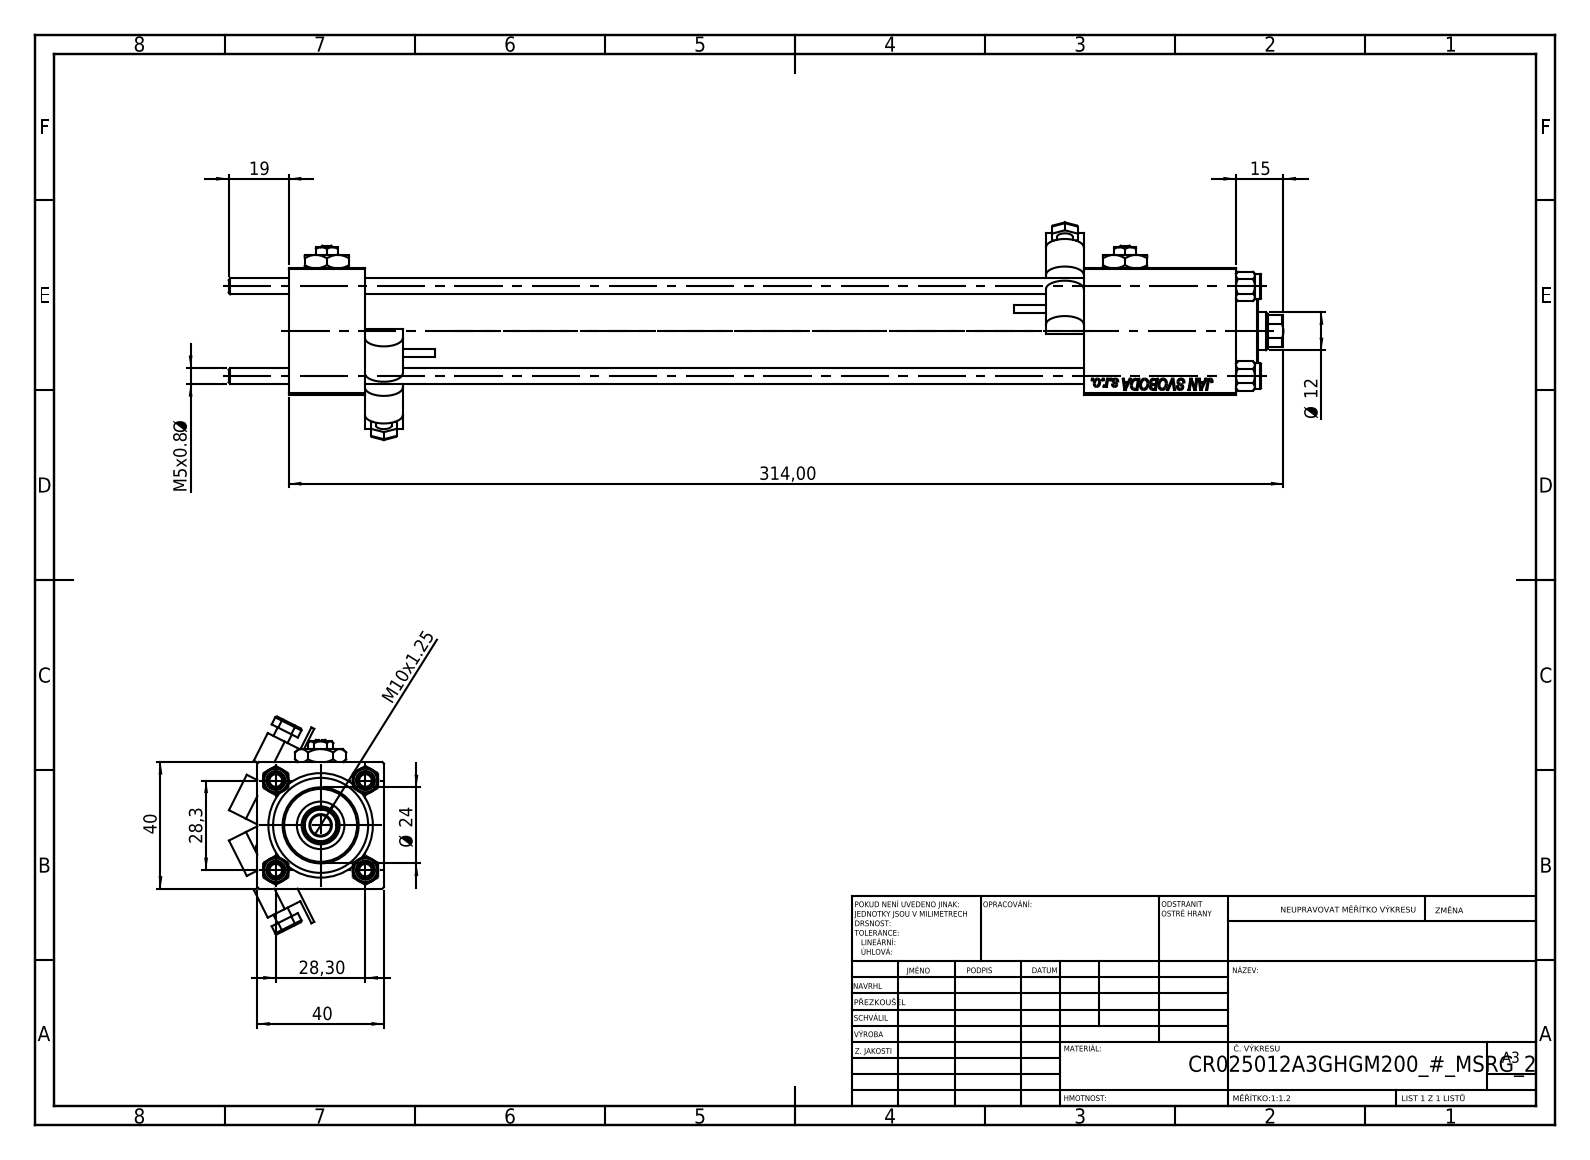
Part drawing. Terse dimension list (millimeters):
name: V215_VC_A; MSRF_MSRG1; Zatka_pro_OIL_PORT; CR025_012_A_0_G_A_G_M_020_+#_##_TYCINKA (+3 more)
written by: SolidWorks 2019 (CONFIG_CONTROL_DESIGN)
unit: mm
bodies: 15 solids, 1296 faces (600 planar, 118 cylindrical, 578 other)
size: 333 × 68.71 × 48.93
volume: 232 318 mm³; area: 114 553 mm²
holes: 4× ⌀5, 3× ⌀20, 2× ⌀7, 2× ⌀13.16, 1× ⌀6.5, 1× ⌀12, 1× ⌀15, 1× ⌀25, 1× ⌀30
bosses: 4× ⌀8, 2× ⌀5, 2× ⌀2.5, 1× ⌀31, 1× ⌀24
rounds: 12× R0.5, 4× R6, 1× R5.5
face distances: 40, 24, 251, 227, 39.8, 299, 275, 48, 270.3, 246.3
hole spacings: 20.01, 28.3, 40.02, 252
